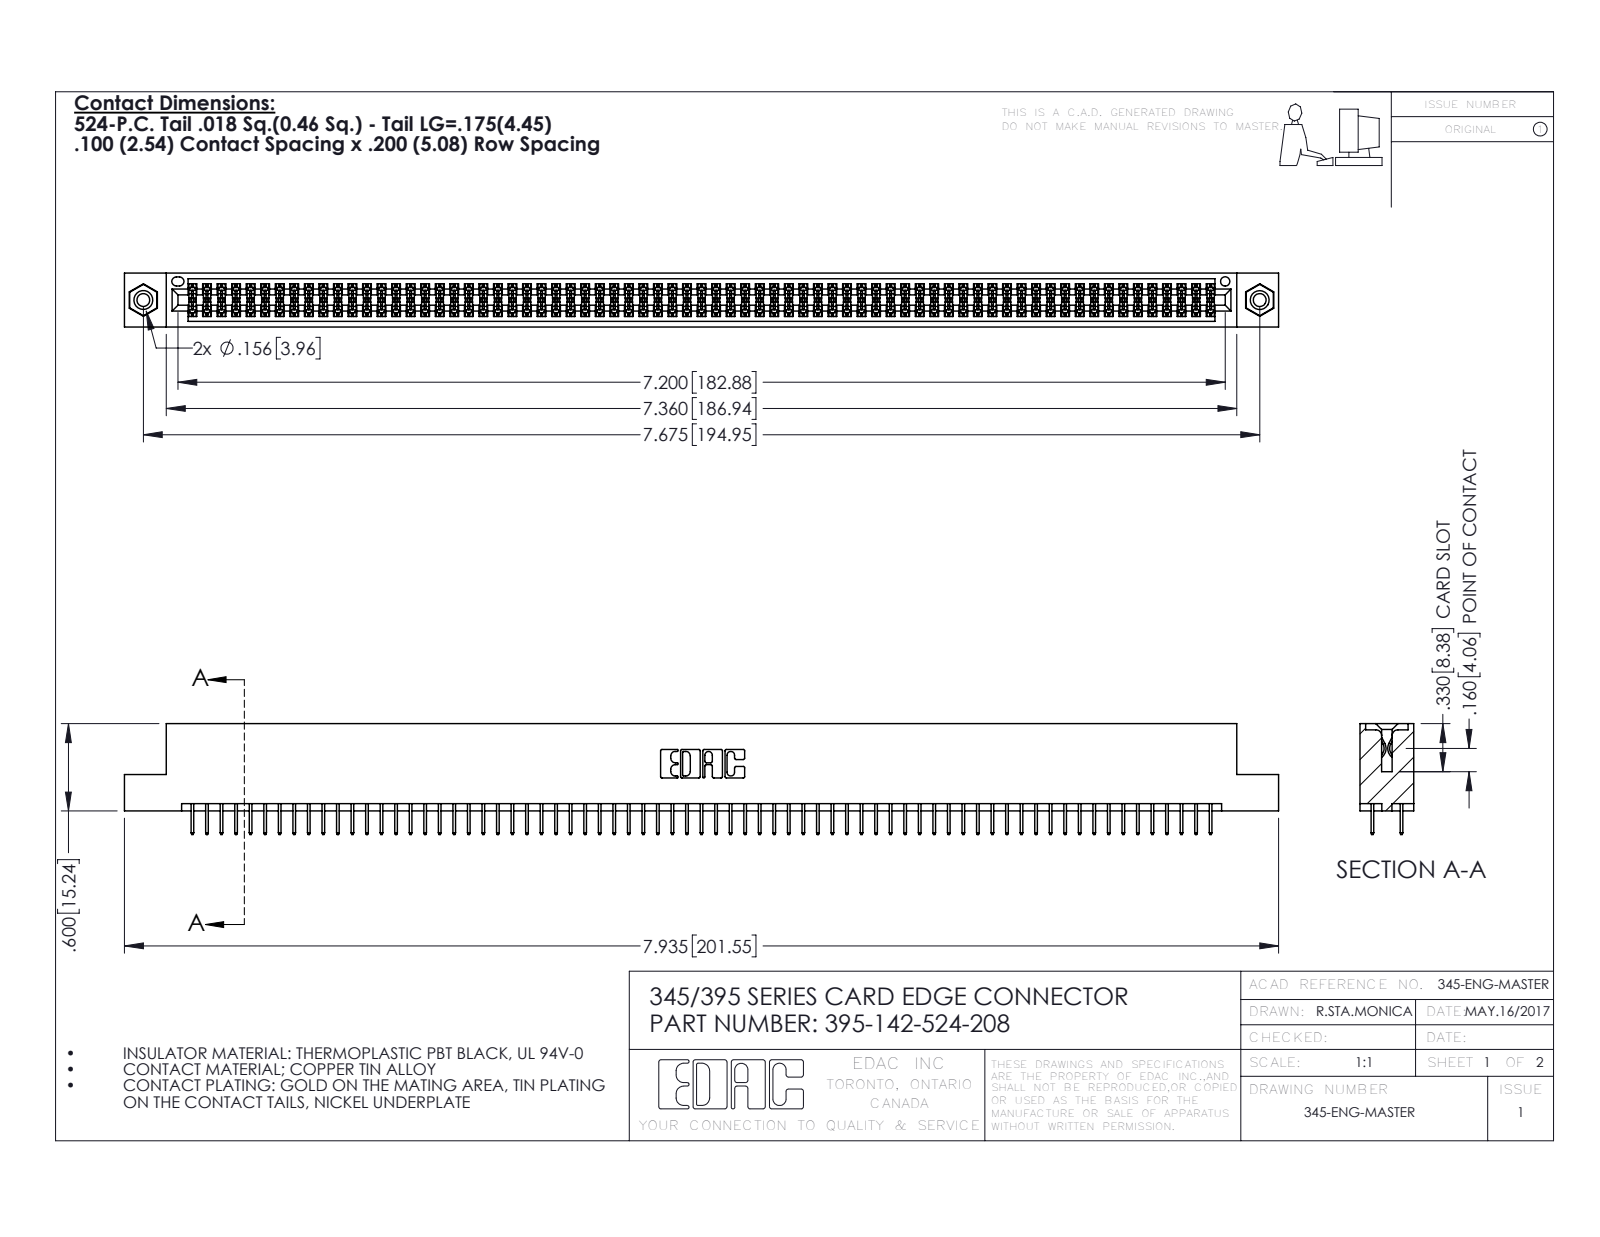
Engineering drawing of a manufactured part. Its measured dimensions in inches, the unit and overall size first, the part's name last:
Units: inches
Overall size (bounding box): 7.935 × 0.762 × 0.37
Round holes (diameter × count): ⌀0.089 ×2, ⌀0.125 ×2, ⌀0.156 ×2, ⌀0.064 ×1
Round bosses / shafts (diameter × count): ⌀0.155 ×2
Partial cylindrical surfaces — rounded edges, fillets, slot ends (radius × count): R0.006 ×213, R0.01 ×22, R0.007 ×6, R0.031 ×6, R0.026 ×3, R0.014 ×2, R0.019 ×2, R0.022 ×2
Main face-to-face distances: 0.072, 0.298, 0.2, 0.37, 0.098, 0.272, 0.025, 0.225, 0.072, 0.175
Hole centre spacings: 0.27, 7.439, 7.675
Volume: 1.198 in³ · Surface area: 44.98 in²
Bodies: 145 solids, 7854 faces (5650 planar, 2188 cylindrical, 16 other)
Part name (STEP PRODUCT): 345 Part_Flush Mounting Lugs - 0.156 Dia-TI; 395-142-524-208; 345-250-001_345-250-003-102; 345-292-001_345-293-124
STEP written by: SolidWorks 2016 (CONFIG_CONTROL_DESIGN)
